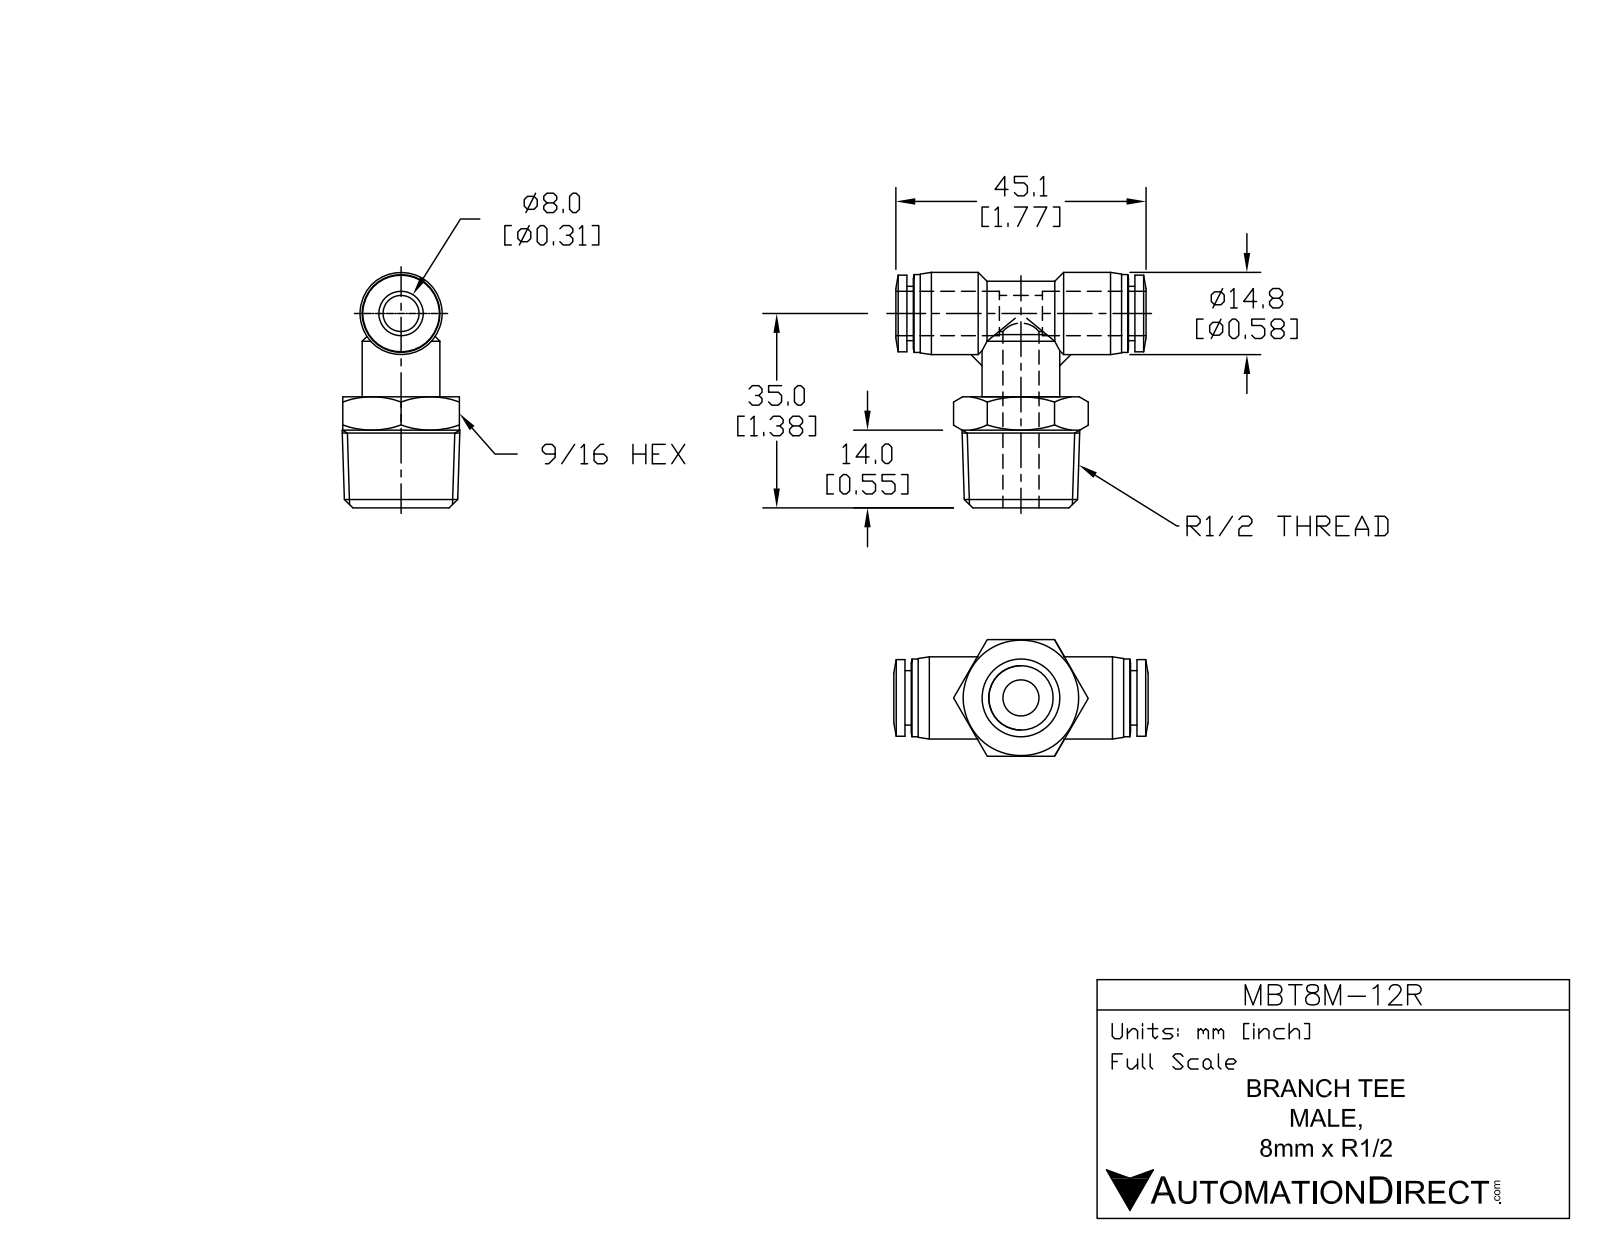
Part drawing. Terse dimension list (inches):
name: MBT8M-12R
written by: SolidWorks 2015 (AUTOMOTIVE_DESIGN)
unit: in
bodies: 1 solid, 99 faces (24 planar, 33 cylindrical, 42 other)
size: 1.78 × 1.673 × 0.827
volume: 0.728 in³; area: 9.861 in²
holes: 2× ⌀0.236, 1× ⌀0.327
bosses: 1× ⌀0.591, 1× ⌀0.559, 1× ⌀0.551, 1× ⌀0.543, 1× ⌀0.457, 1× ⌀0.386
rounds: 1× R0.228
face distances: 0.827, 0.787, 0.045, 1.577, 1.622, 0.642, 0.98, 0.596, 0.935, 1.531
